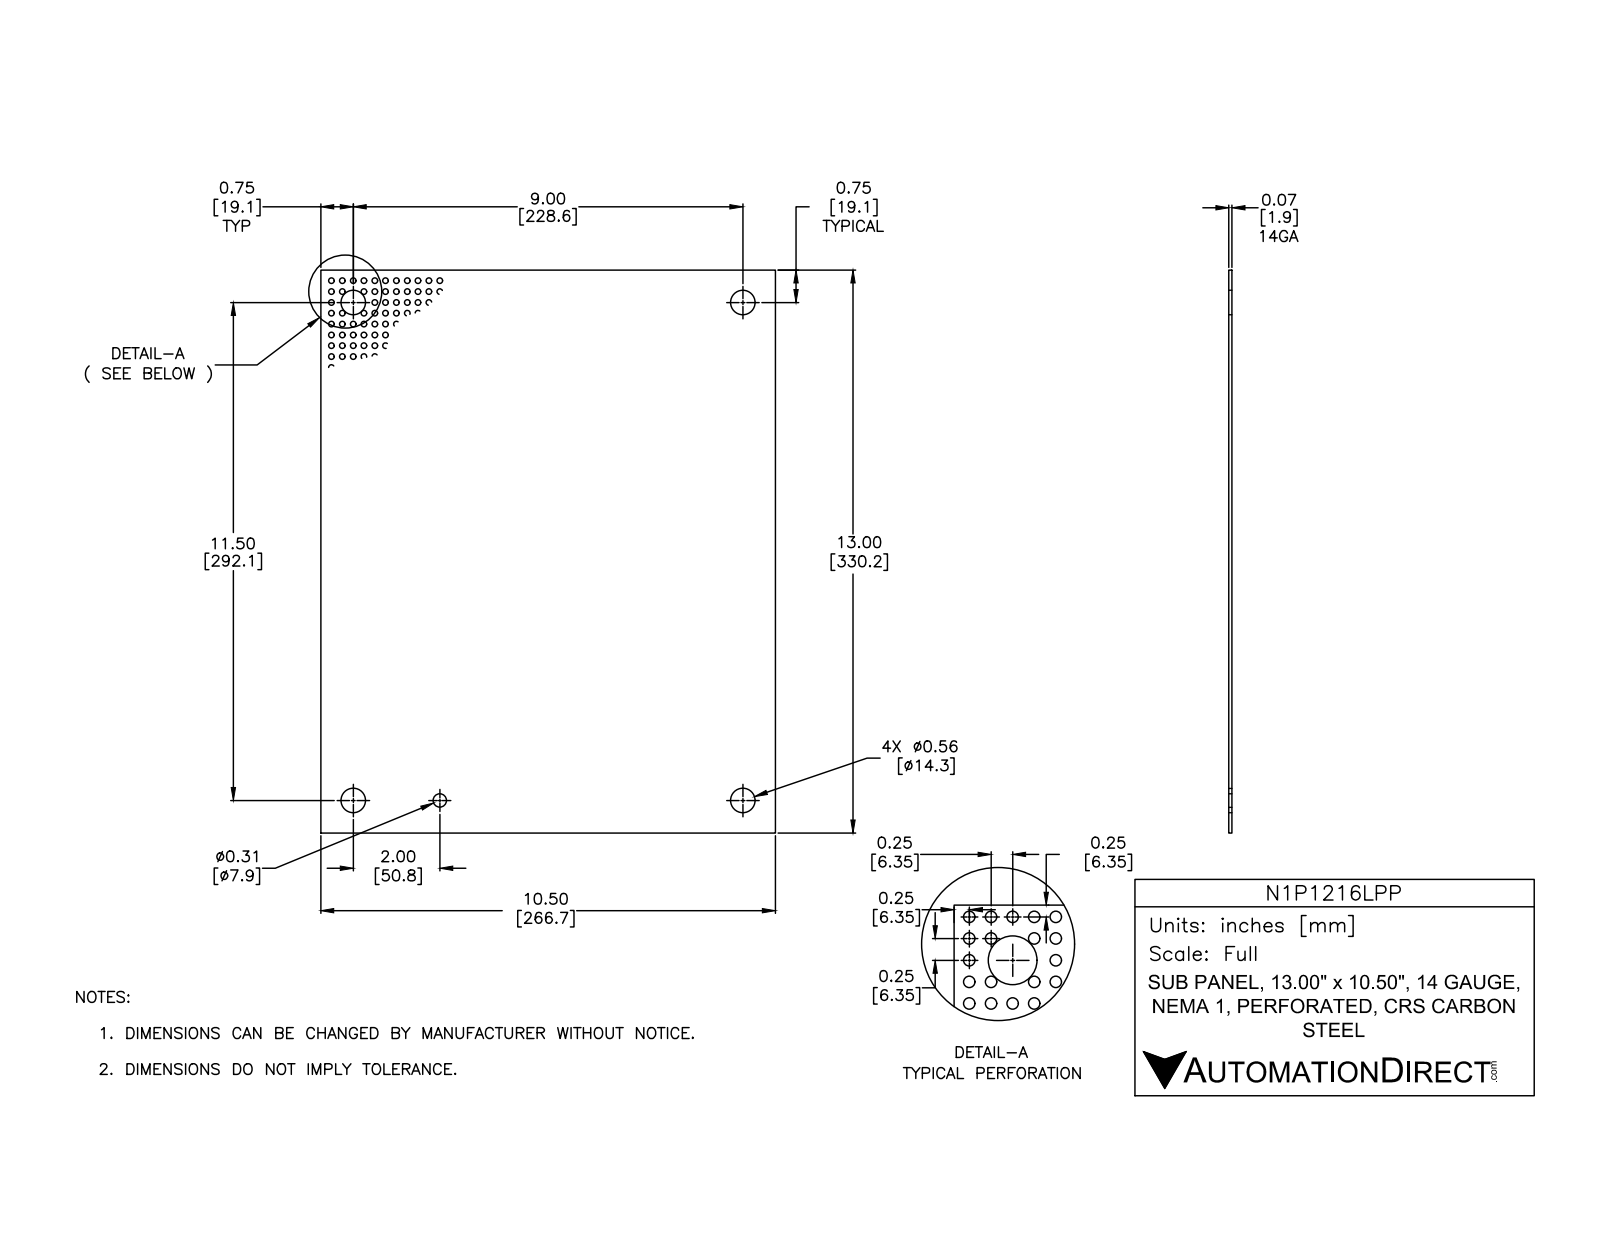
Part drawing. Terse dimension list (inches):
name: N1P_PP-LARGE
written by: Autodesk Inventor 2012 (AUTOMOTIVE_DESIGN)
unit: in
bodies: 1 solid, 11 faces (6 planar, 5 cylindrical, 0 other)
size: 13 × 10.5 × 0.074
volume: 10.02 in³; area: 274.9 in²
holes: 4× ⌀0.563, 1× ⌀0.312
face distances: 0.074, 10.5, 13
hole spacings: 9, 11.5, 14.603, 2, 7, 11.672, 13.463
